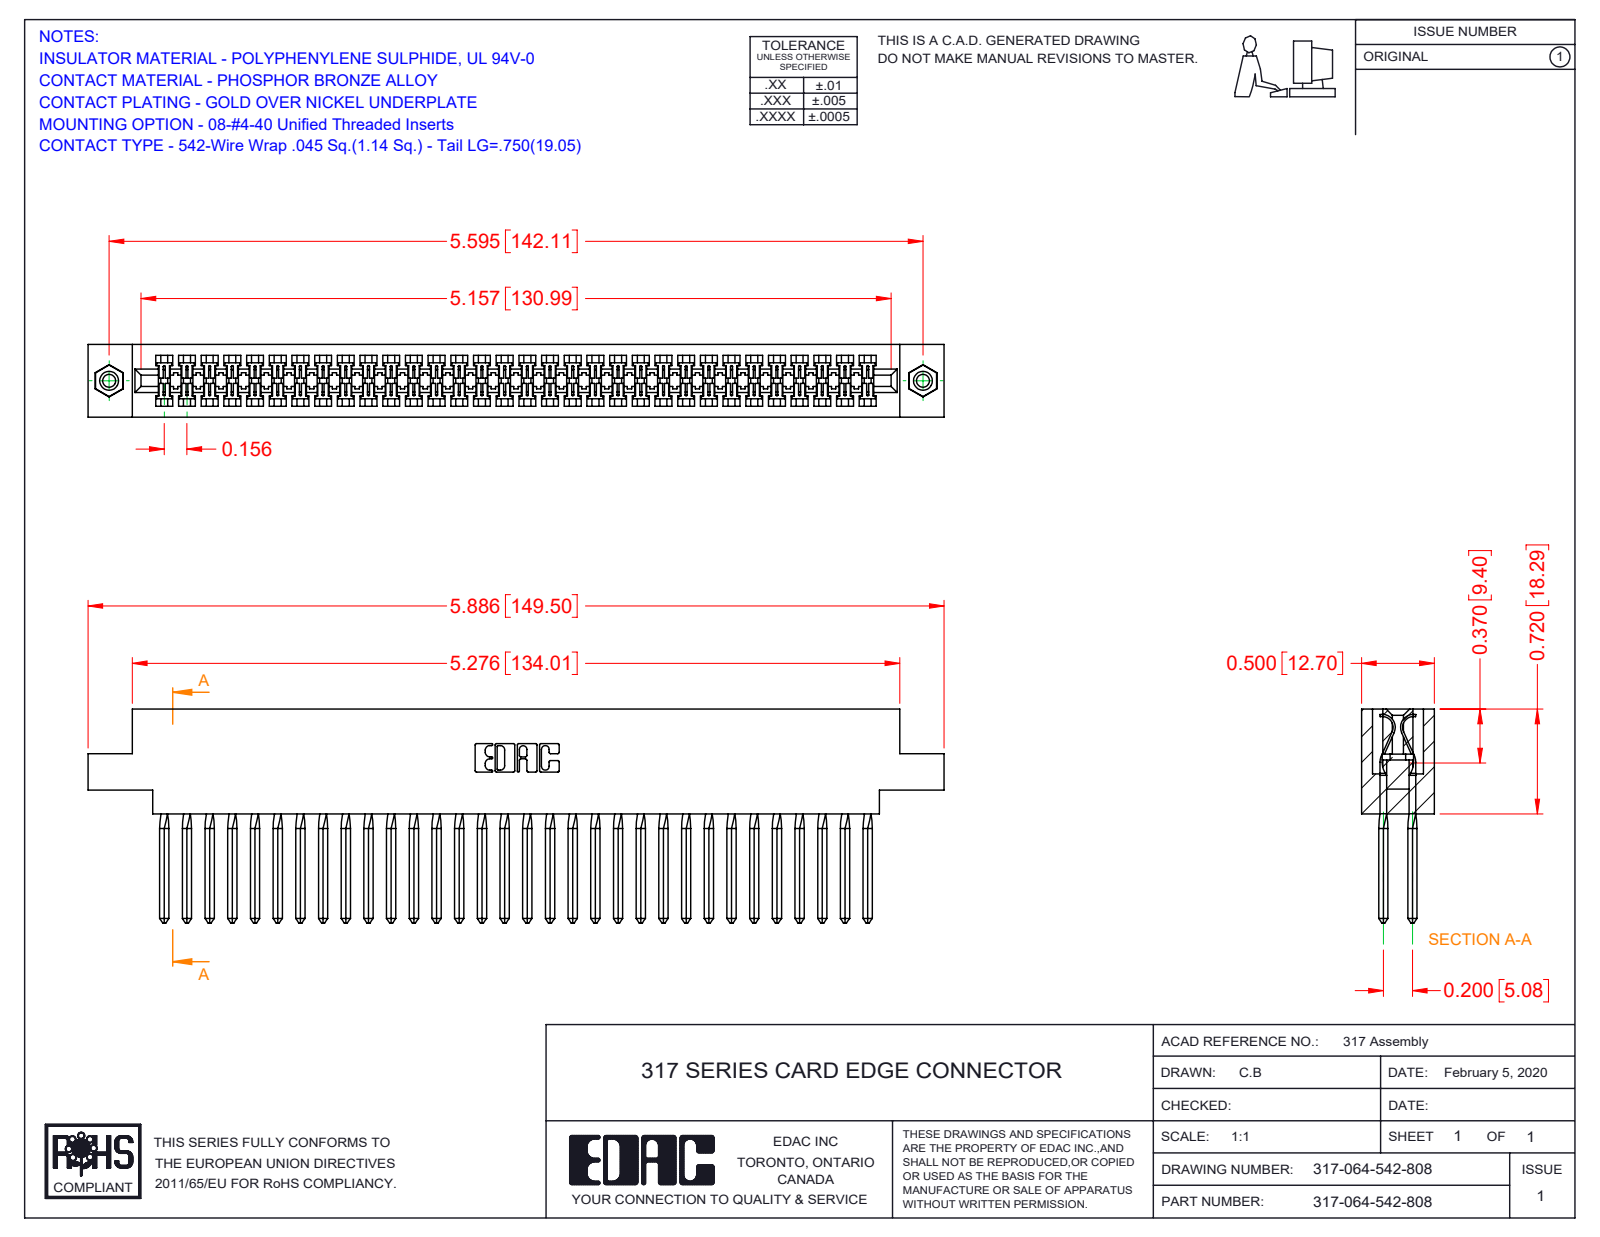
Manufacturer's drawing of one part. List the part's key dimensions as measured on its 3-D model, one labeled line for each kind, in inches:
Part name (STEP PRODUCT): 317-064-542-878; 345-250-001_345-250-003-102; 317 Part_.156 Dia - TI; 317-290-003_542
STEP written by: SolidWorks 2016 (CONFIG_CONTROL_DESIGN)
Units: inches
Bodies: 67 solids, 3810 faces (3034 planar, 504 cylindrical, 272 other)
Overall size (bounding box): 5.886 × 1.47 × 0.5
Volume: 1.474 in³ · Surface area: 51.61 in²
Round holes (diameter × count): ⌀0.089 ×2, ⌀0.125 ×2, ⌀0.156 ×2
Round bosses / shafts (diameter × count): ⌀0.155 ×2
Partial cylindrical surfaces — rounded edges, fillets, slot ends (radius × count): R0.006 ×128, R0.01 ×22, R0.007 ×6, R0.031 ×6, R0.026 ×3, R0.074 ×2, R0.089 ×2, R0.1 ×2
Main face-to-face distances: 0.5, 0.075, 0.425, 0.35, 0.2, 0.116, 0.11, 0.046, 0.128, 0.372
Hole centre spacings: 5.595
